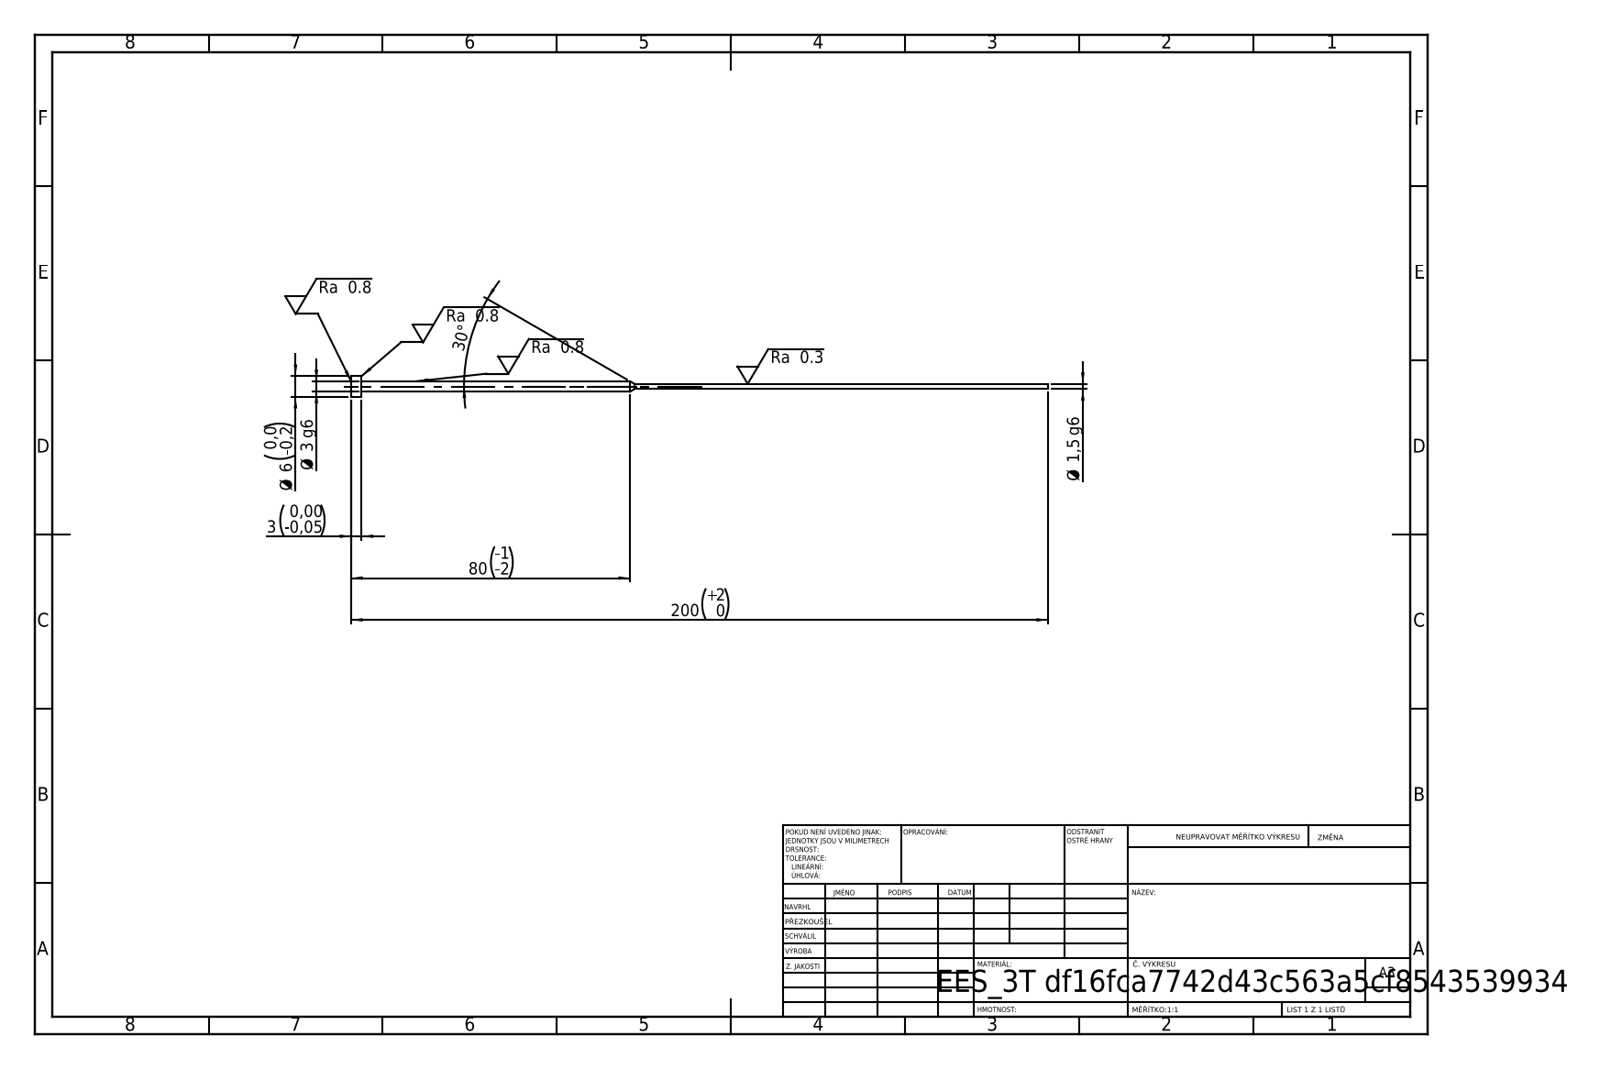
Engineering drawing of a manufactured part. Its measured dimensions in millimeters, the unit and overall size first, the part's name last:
Units: millimetres
Overall size (bounding box): 200 × 6 × 6
Round bosses / shafts (diameter × count): ⌀6 ×1, ⌀3 ×1, ⌀1.5 ×1
Main face-to-face distances: 3, 197, 200
Volume: 844 mm³ · Surface area: 1 403 mm²
Bodies: 1 solid, 11 faces (3 planar, 6 cylindrical, 2 other)
STEP written by: SolidWorks 2019 (CONFIG_CONTROL_DESIGN)
